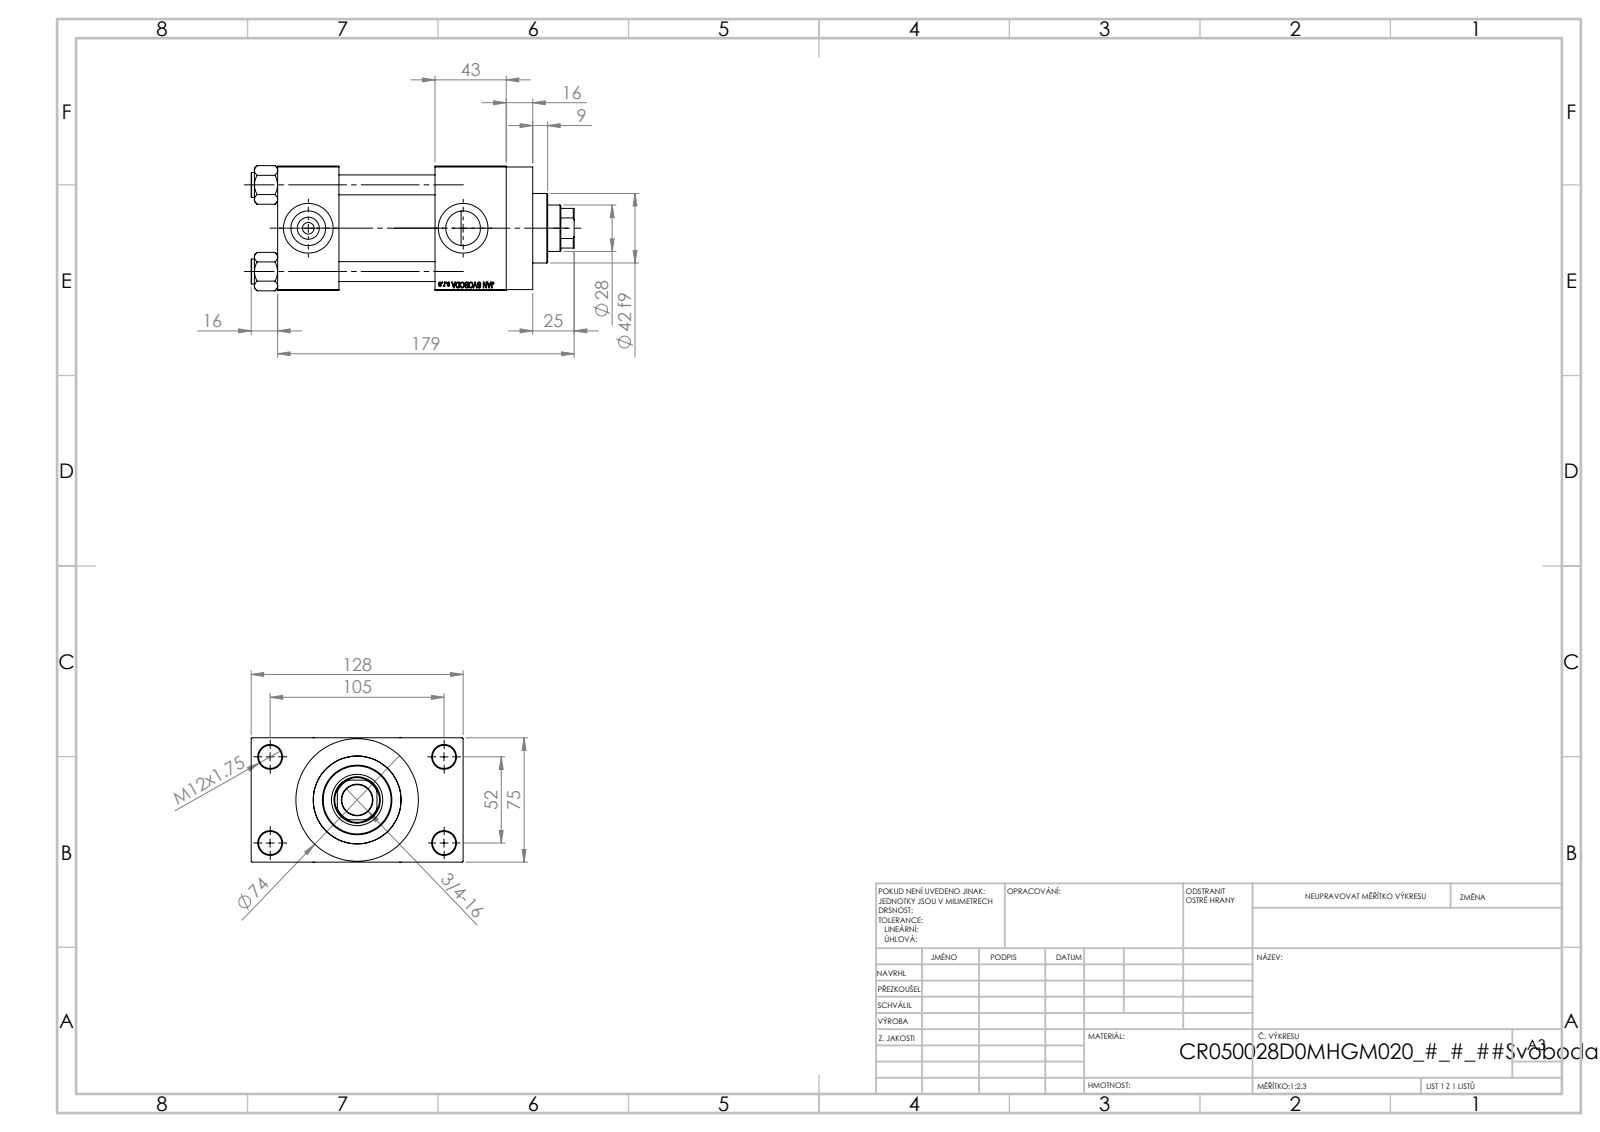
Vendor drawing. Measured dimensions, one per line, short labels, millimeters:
name: V215CR_D_TYCINKA; V215CR_D_Body; V215CR_VCP_D; NUT_M5_D (+1 more)
written by: SolidWorks 2019 (CONFIG_CONTROL_DESIGN)
unit: mm
bodies: 11 solids, 1103 faces (497 planar, 88 cylindrical, 518 other)
size: 195 × 128 × 75.54
volume: 806 210 mm³; area: 170 608 mm²
holes: 4× ⌀12, 4× ⌀14, 2× ⌀7, 2× ⌀20.96, 2× ⌀30, 1× ⌀18.5, 1× ⌀28, 1× ⌀31, 1× ⌀41, 1× ⌀50, 1× ⌀53
bosses: 4× ⌀15, 1× ⌀74, 1× ⌀56, 1× ⌀42
rounds: 1× R13.5
face distances: 75, 58, 37, 95, 26.5, 138, 101, 43, 101.5, 16
hole spacings: 26.35, 36.98, 52.3, 58.43, 58.59, 78.65, 94.37, 52
